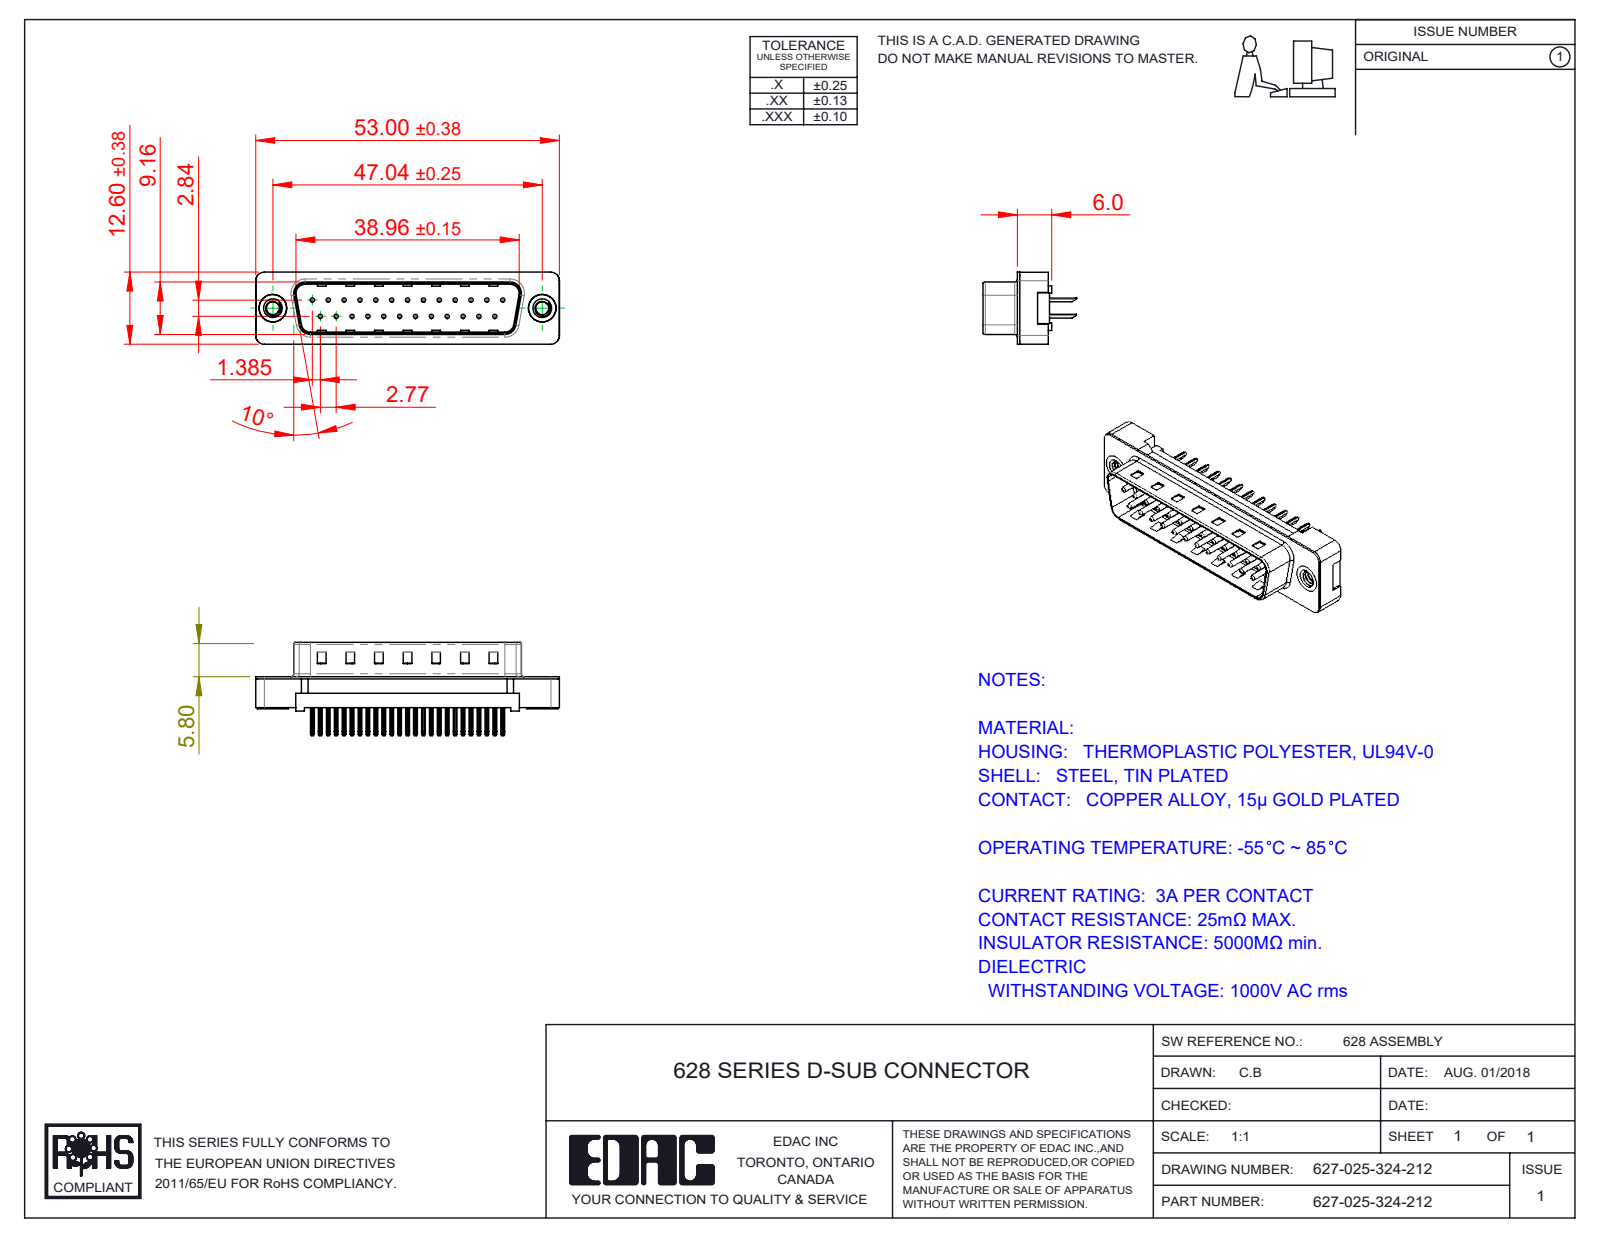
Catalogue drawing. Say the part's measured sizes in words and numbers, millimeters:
The part is named "627 PB Contact Row 2_24; 627 PB Contact Row 1_24; 627-025-324-212; 627 Plastic Body Housing_25 Contacts (+2 more)". Its 3-D file was written by "SolidWorks 2020 (CONFIG_CONTROL_DESIGN)". It is 29 solids with 1767 faces: 1153 planar, 504 cylindrical and 110 other. Overall it measures 53.04 by 16.3 by 12.6 millimeters. Its volume is 2 554 cubic millimeters and its surface area 5 912 square millimeters. Round holes: 25 of diameter 0.35, 25 of diameter 0.85, 2 of diameter 2.26, 2 of diameter 4, 2 of diameter 4.8, 2 of diameter 5. Round bosses or shafts: 25 of diameter 0.75, 2 of diameter 4.9. Partial cylindrical surfaces (rounded edges, fillets, slot ends): 50 of radius 0.25, 25 of radius 0.12, 8 of radius 0.5, 8 of radius 1.5, 4 of radius 0.9, 4 of radius 1.6, 4 of radius 2, 2 of radius 0.4. The main face-to-face distances are 0.4, 2.5, 8.76, 5.4, 2.9, 5, 8.48, 1.58, 1.3, 0.68. The hole center spacings are 3.16, 5.54, 2.77, 11.08, 8.31, 5.03, 13.85, 16.62.
